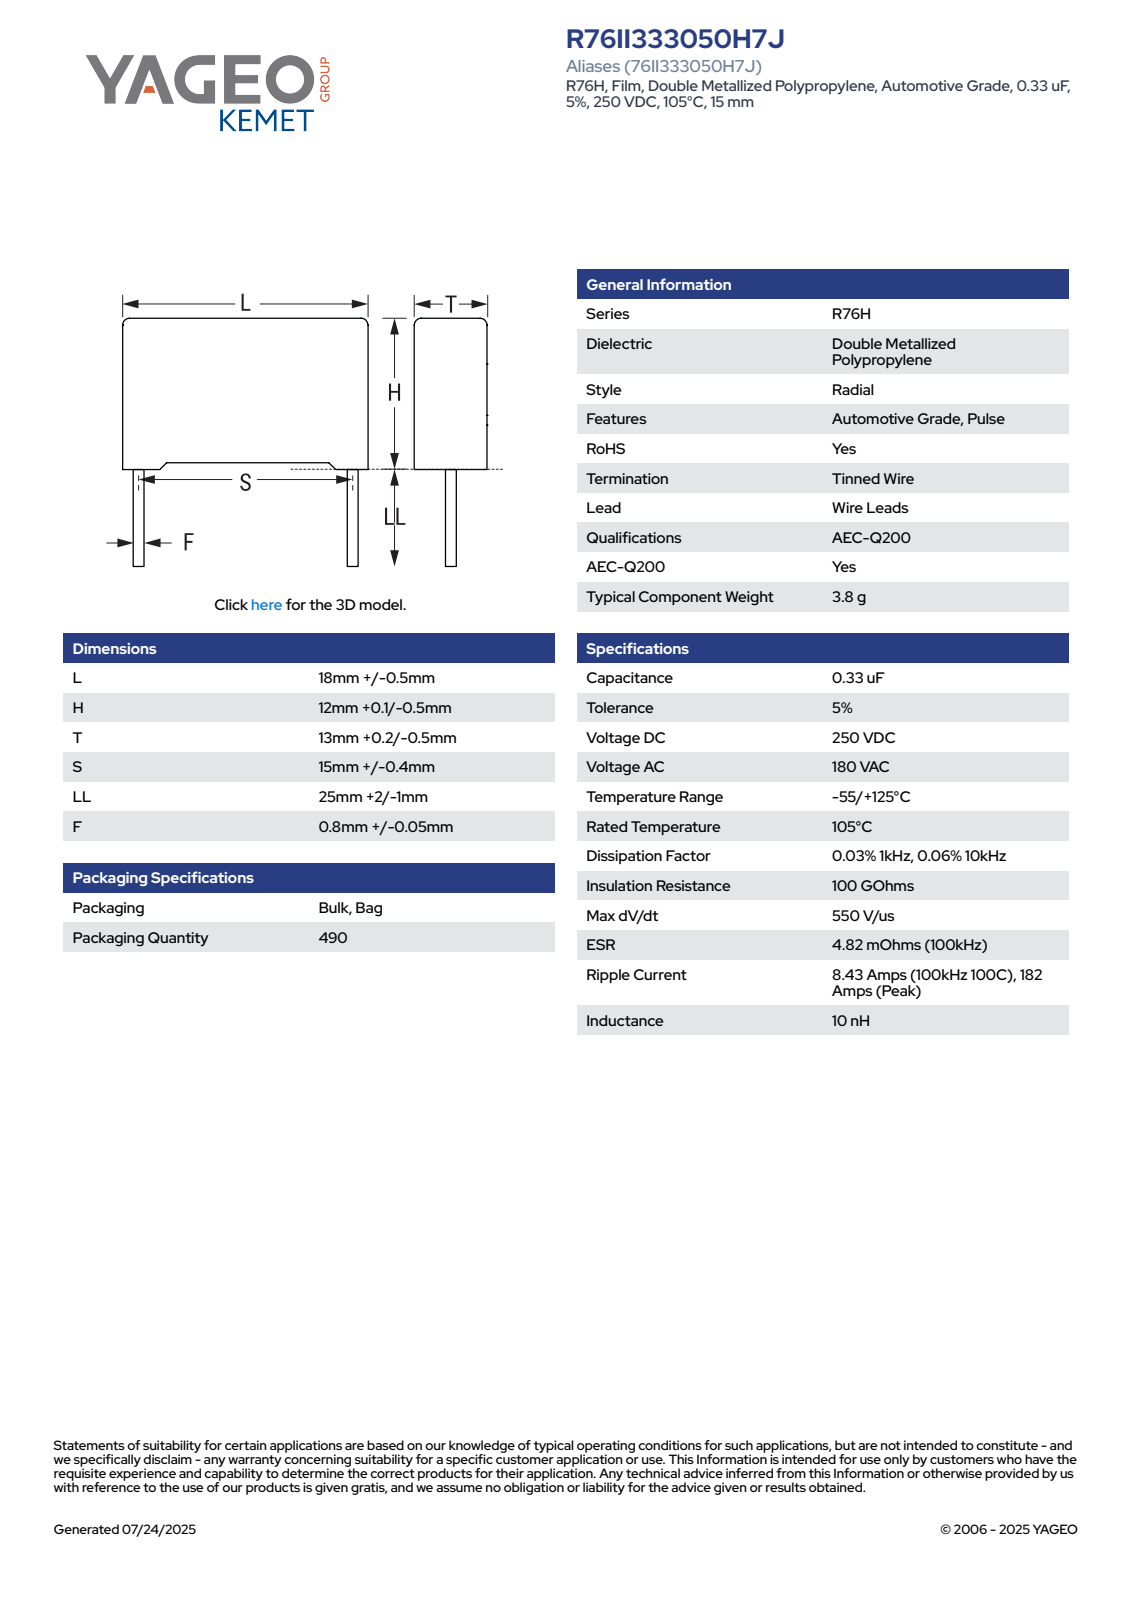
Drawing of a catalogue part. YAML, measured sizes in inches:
part_name: "CFR_RB2R76_18X12X13_L18.5H12.1T13.2S15LL27F0.85"
step_written_by: "SolidWorks 2014 (AUTOMOTIVE_DESIGN)"
units: inches
bodies: {solids: 4, faces: 85, planar: 77, cylindrical: 8, other: 0}
overall_size: [1.539, 0.728, 0.52]
volume: 0.172
surface_area: 2.234
round_bosses_or_shafts:
  - {diameter: 0.033, count: 2}
partial_cylinders:
  - {radius: 0.02, count: 4}
face_to_face_distances: [0.52, 0.447, 0.728, 0.024, 0.03, 0.476, 0.704, 0.495, 0.017, 0.013]
